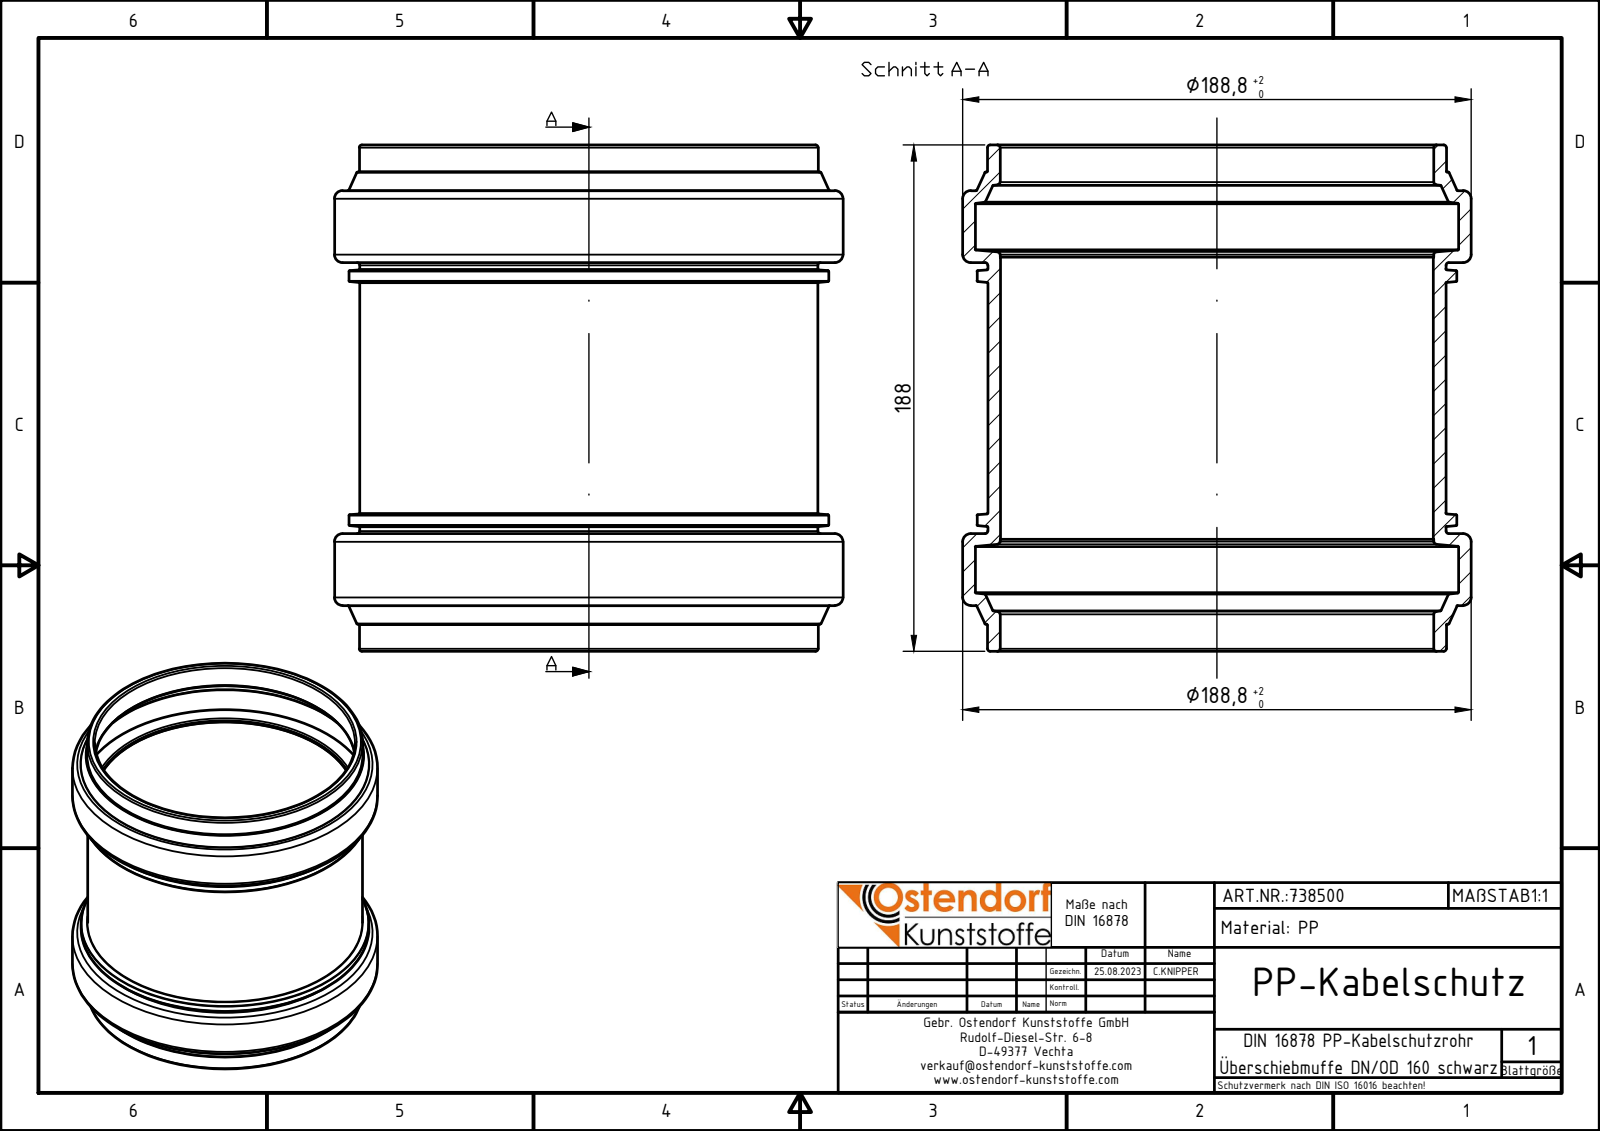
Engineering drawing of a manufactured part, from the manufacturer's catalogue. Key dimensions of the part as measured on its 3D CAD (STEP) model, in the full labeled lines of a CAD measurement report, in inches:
Part name (STEP PRODUCT): 738500z
STEP written by: Autodesk Inventor 2024 (AUTOMOTIVE_DESIGN)
Units: inches
Bodies: 1 solid, 76 faces (10 planar, 16 cylindrical, 50 other)
Overall size (bounding box): 7.433 × 7.433 × 7.402
Volume: 34.48 in³ · Surface area: 375.7 in²
Round holes (diameter × count): ⌀6.327 ×1, ⌀6.339 ×1, ⌀7.063 ×1
Round bosses / shafts (diameter × count): ⌀7.433 ×1, ⌀7.012 ×1, ⌀6.709 ×1, ⌀6.697 ×1
Main face-to-face distances: 3.961, 1.72, 5.681, 0.669, 6.732, 1.051, 5.012, 7.402, 6.063, 0.397
